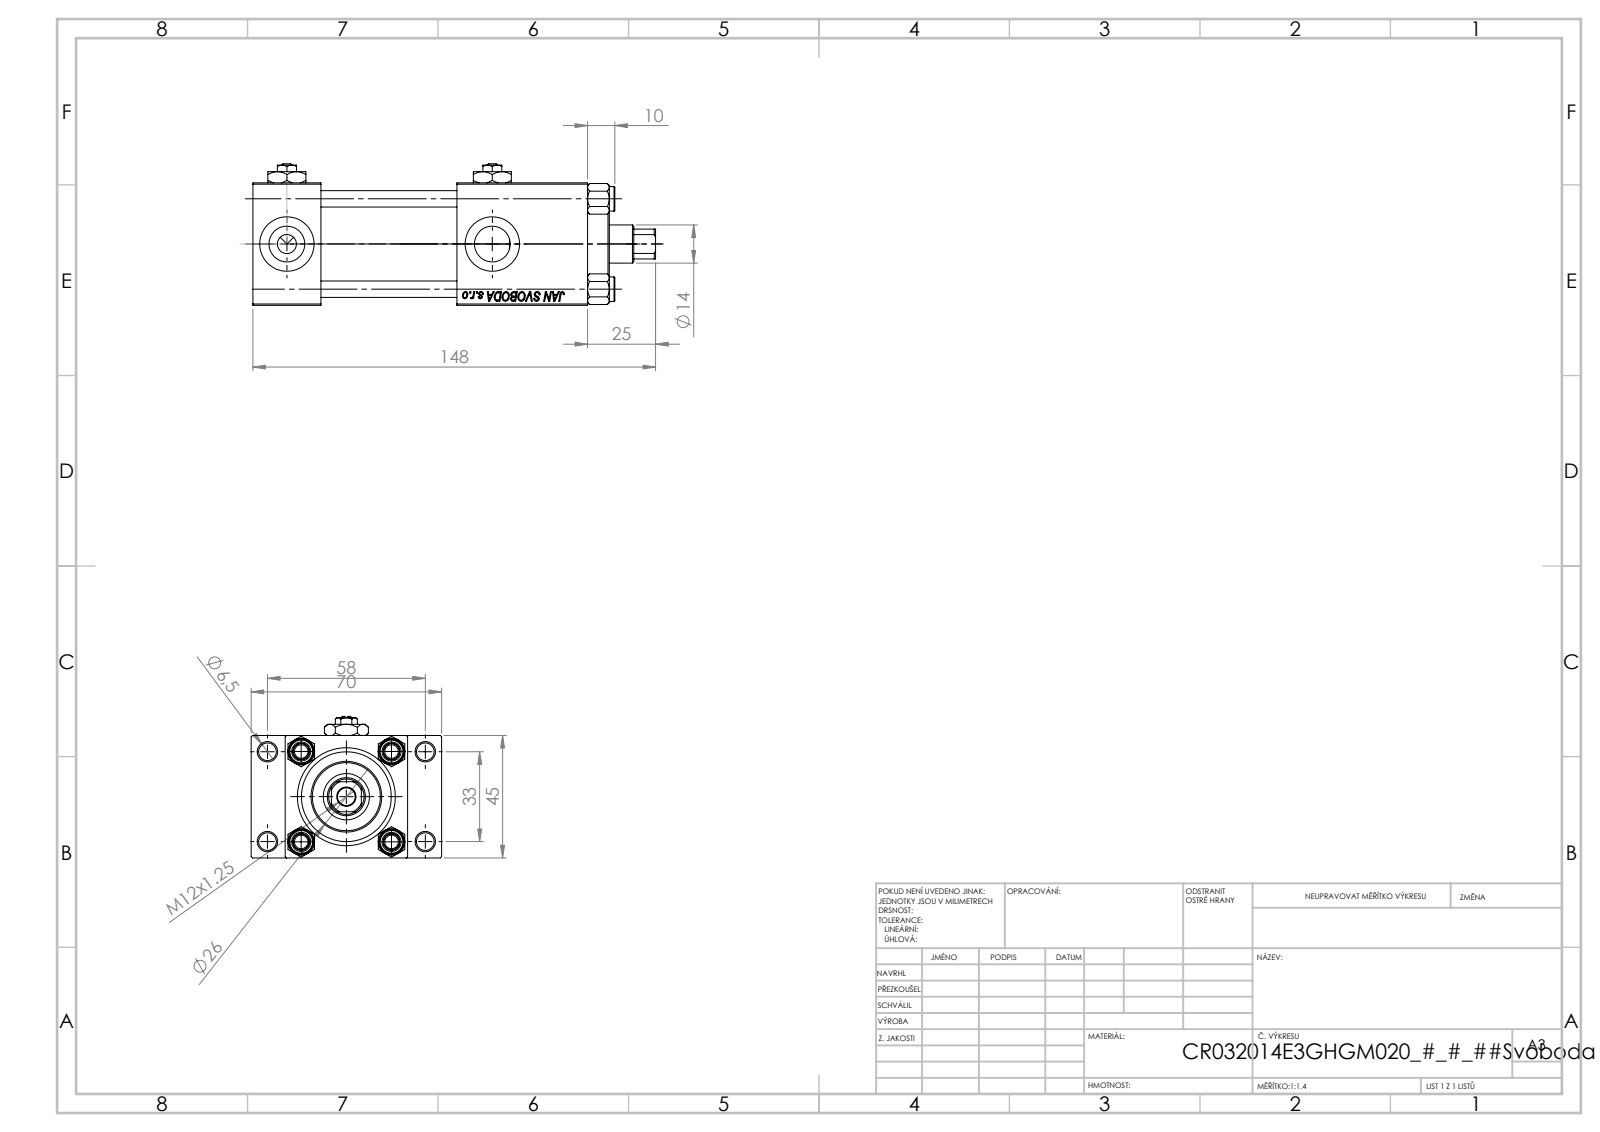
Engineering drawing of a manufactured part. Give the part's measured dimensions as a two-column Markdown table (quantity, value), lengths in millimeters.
| quantity | value |
| --- | --- |
| part name | V215CR_VCP_E; V215_VC_A; Zatka_pro_OIL_PORT; V215CR_TYCINKA_E (+2 more) |
| STEP written by | SolidWorks 2019 (CONFIG_CONTROL_DESIGN) |
| units | millimeters |
| bodies | 13 solids, 1235 faces (544 planar, 97 cylindrical, 594 other) |
| overall size | 148 × 70 × 52 |
| volume | 217 794 mm³ |
| surface area | 78 247 mm² |
| round holes (diameter × count) | 6.5 × 5, 6 × 4, 13.16 × 4, 20 × 4, 7 × 3, 14 × 1, 17 × 1, 24 × 1, 32 × 1, 33 × 1 |
| round bosses / shafts (diameter × count) | 9 × 4, 38 × 1, 26 × 1 |
| partial cylindrical surfaces (radius × count) | 6.5 × 1 |
| main face-to-face distances | 45, 25, 12.5, 57.5, 123, 98, 50, 75, 48, 94.3 |
| hole center spacings | 12.4, 23.48, 33.2, 33.37, 35.35, 45.6, 56.35, 33 |
